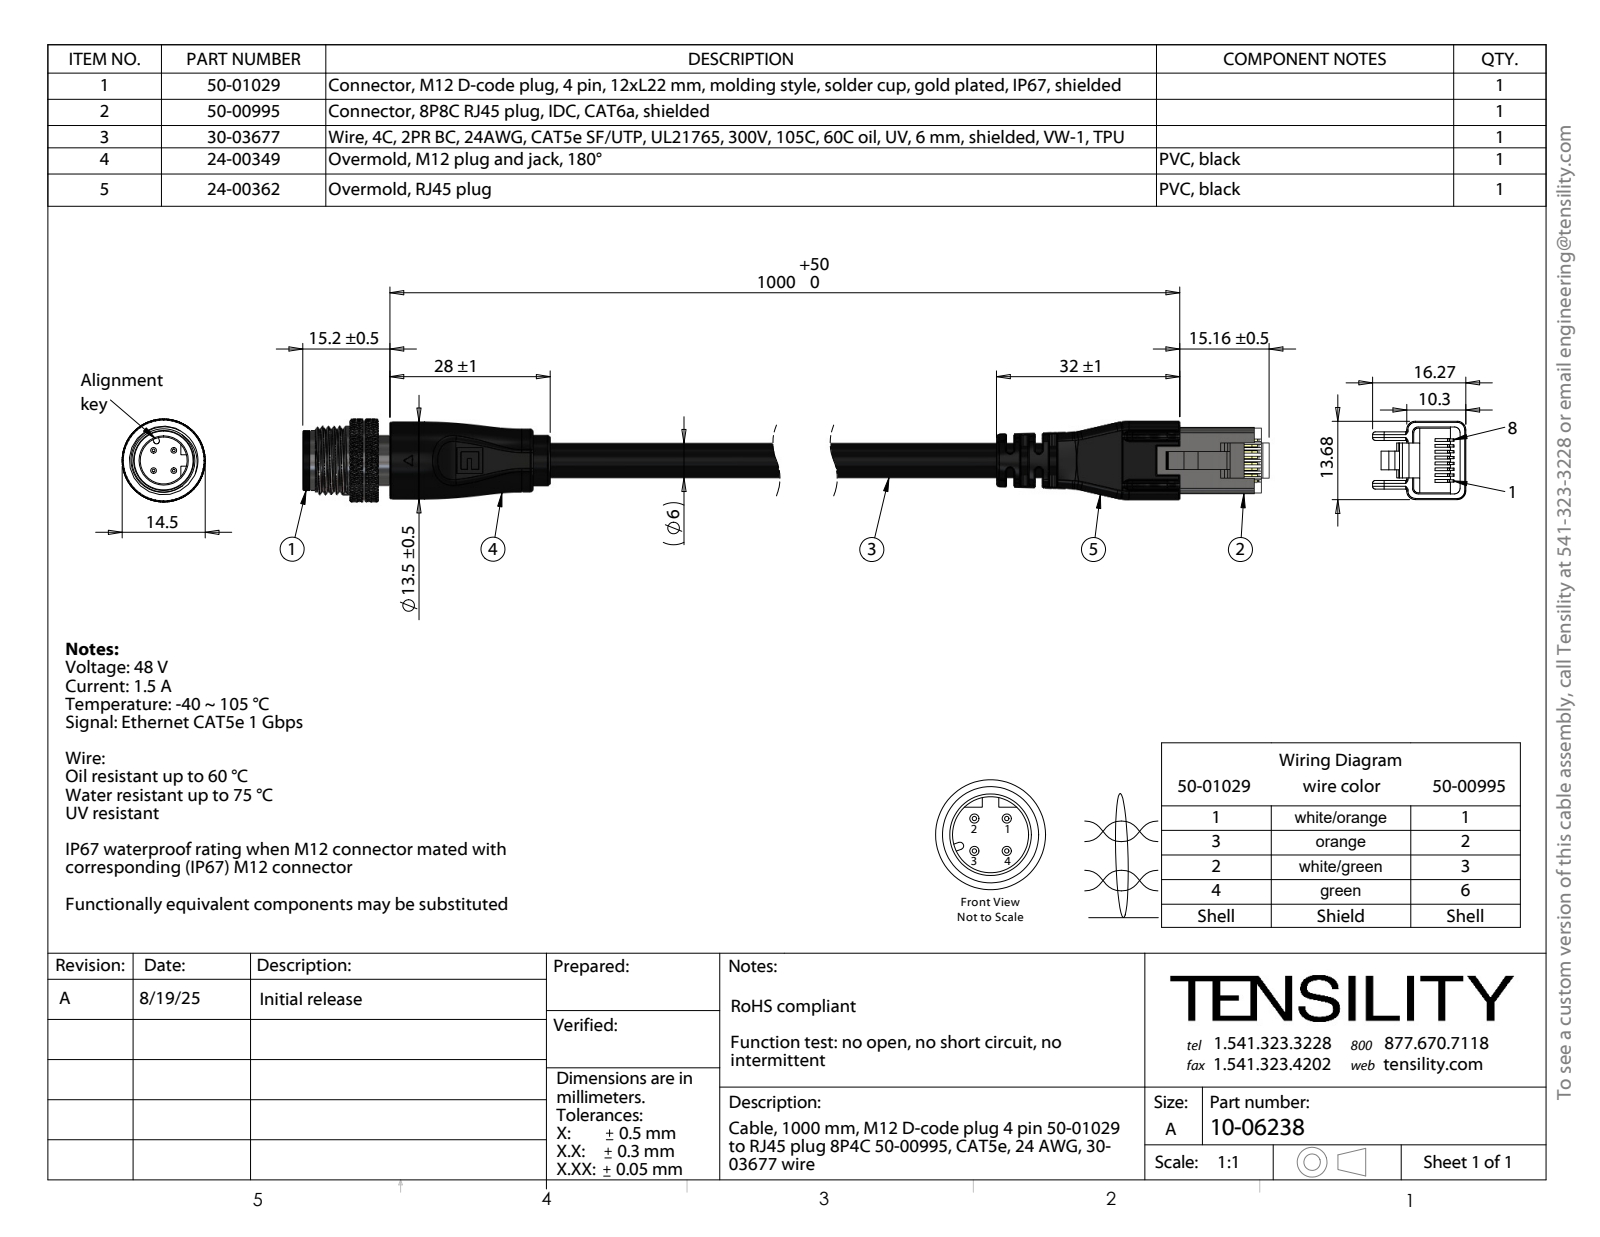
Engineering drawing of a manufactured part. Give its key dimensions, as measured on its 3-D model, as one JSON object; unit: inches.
{"part_name": "50-00995; 30-03677_blunt cut; 50-01029-01_默认; 50-01029_默认 (+6 more)", "step_written_by": "SolidWorks 2025 (CONFIG_CONTROL_DESIGN)", "units": "inches", "bodies": {"solids": 54, "faces": 3209, "planar": 470, "cylindrical": 811, "other": 1928}, "overall_size": [9.067, 0.723, 0.571], "volume_in3": 0.849, "surface_area_in2": 45.15, "round_holes": [[0.008, 28], [0.039, 4], [0.041, 4], [0.124, 1], [0.126, 1], [0.14, 1], [0.315, 1], [0.323, 1], [0.346, 1], [0.374, 1]], "round_bosses_or_shafts": [[0.055, 4], [0.571, 1], [0.547, 1], [0.531, 1], [0.472, 1], [0.433, 1], [0.413, 1], [0.366, 1]], "partial_cylinders_radius": [[0.008, 11], [0.02, 10], [0.059, 10], [0.024, 8], [0.039, 5], [0.394, 4], [0.031, 2], [0.045, 2]], "face_to_face_distances": [0.049, 0.098, 0.039, 0.148, 0.197, 0.366, 0.276, 7.854, 0.499, 0.46], "hole_center_spacings": [0.042, 0.075, 0.082, 0.014, 0.043, 0.067, 0.071, 0.089]}
